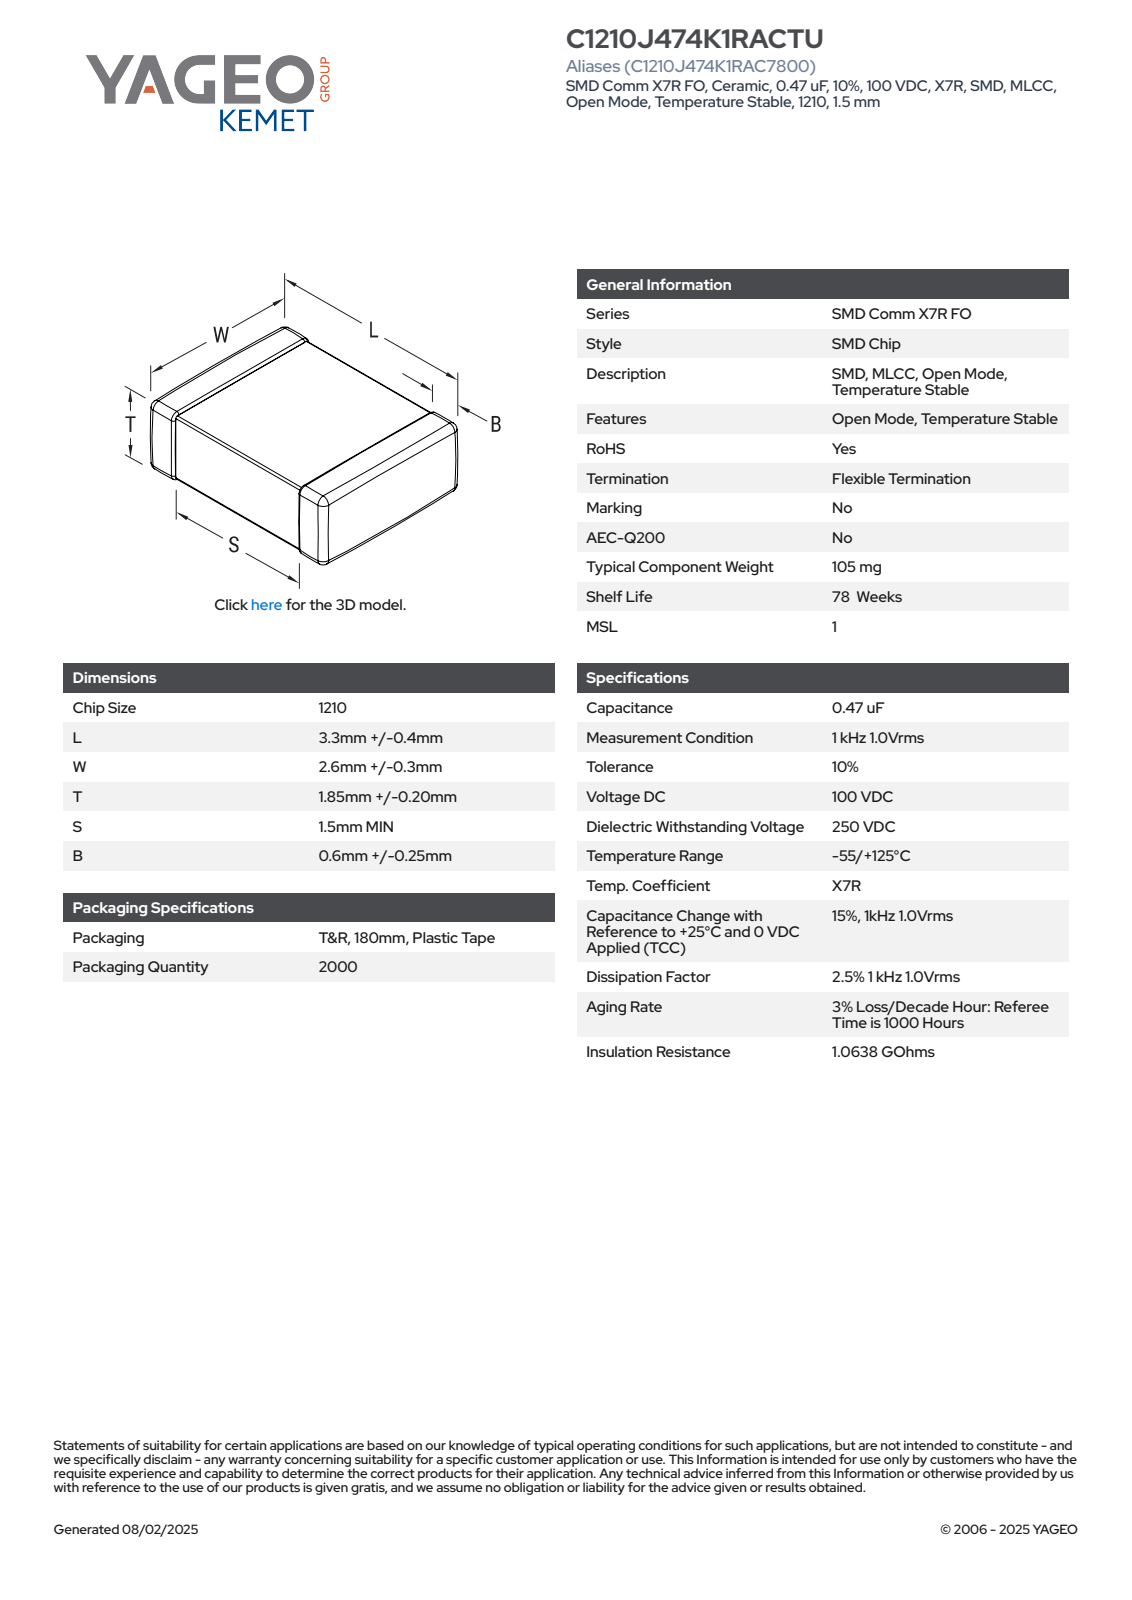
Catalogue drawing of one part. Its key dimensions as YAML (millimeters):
part_name: "CCS_CCSTD_1210_L3.7W2.9T2.05B0.6"
step_written_by: "SolidWorks 2021 (AUTOMOTIVE_DESIGN)"
units: millimeters
bodies: {solids: 4, faces: 125, planar: 71, cylindrical: 38, other: 16}
overall_size: [3.7, 2.9, 2.05]
volume: 21
surface_area: 48
face_to_face_distances: [1.99, 2.84, 3.7, 1.93, 2.05, 2.78, 2.9, 0.43, 1.57, 2.13]
